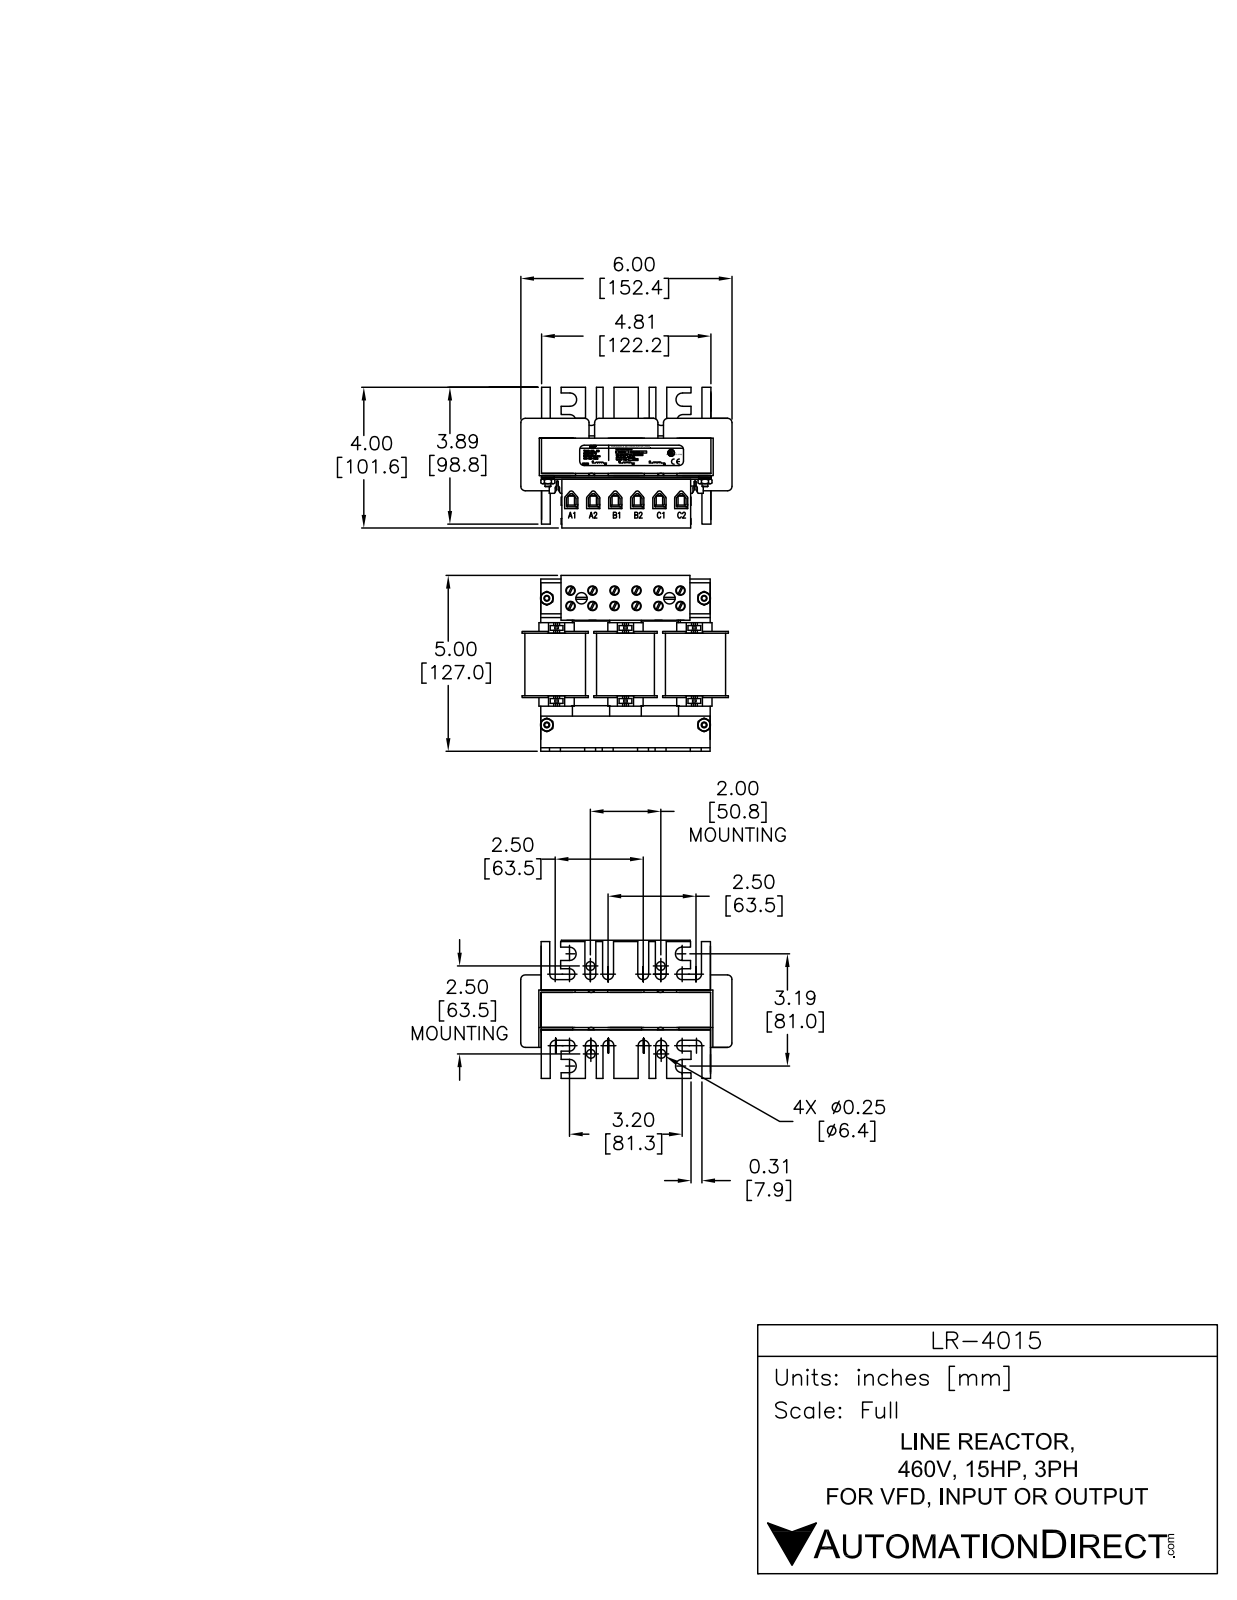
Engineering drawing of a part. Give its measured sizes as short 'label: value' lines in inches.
name: LR-4015
written by: SolidWorks 2011 (AUTOMOTIVE_DESIGN)
unit: in
bodies: 43 solids, 1048 faces (794 planar, 222 cylindrical, 32 other)
size: 5.699 × 5.165 × 3.873
volume: 33.01 in³; area: 259 in²
holes: 12× ⌀0.276, 5× ⌀0.305
bosses: 12× ⌀0.276, 4× ⌀0.404, 4× ⌀0.315, 2× ⌀0.305, 2× ⌀0.295, 2× ⌀0.134, 2× ⌀0.128
rounds: 16× R0.155, 12× R0.072, 12× R0.106, 12× R0.107, 12× R0.197, 12× R0.236, 4× R0.19, 3× R0.034
face distances: 0.098, 1.073, 0.059, 1.23, 0.221, 1.373, 1.132, 1.354, 0.28, 1.294
hole spacings: 0.63, 1.26, 0.837, 1.375, 1.89, 0.551, 1.969, 0.407
